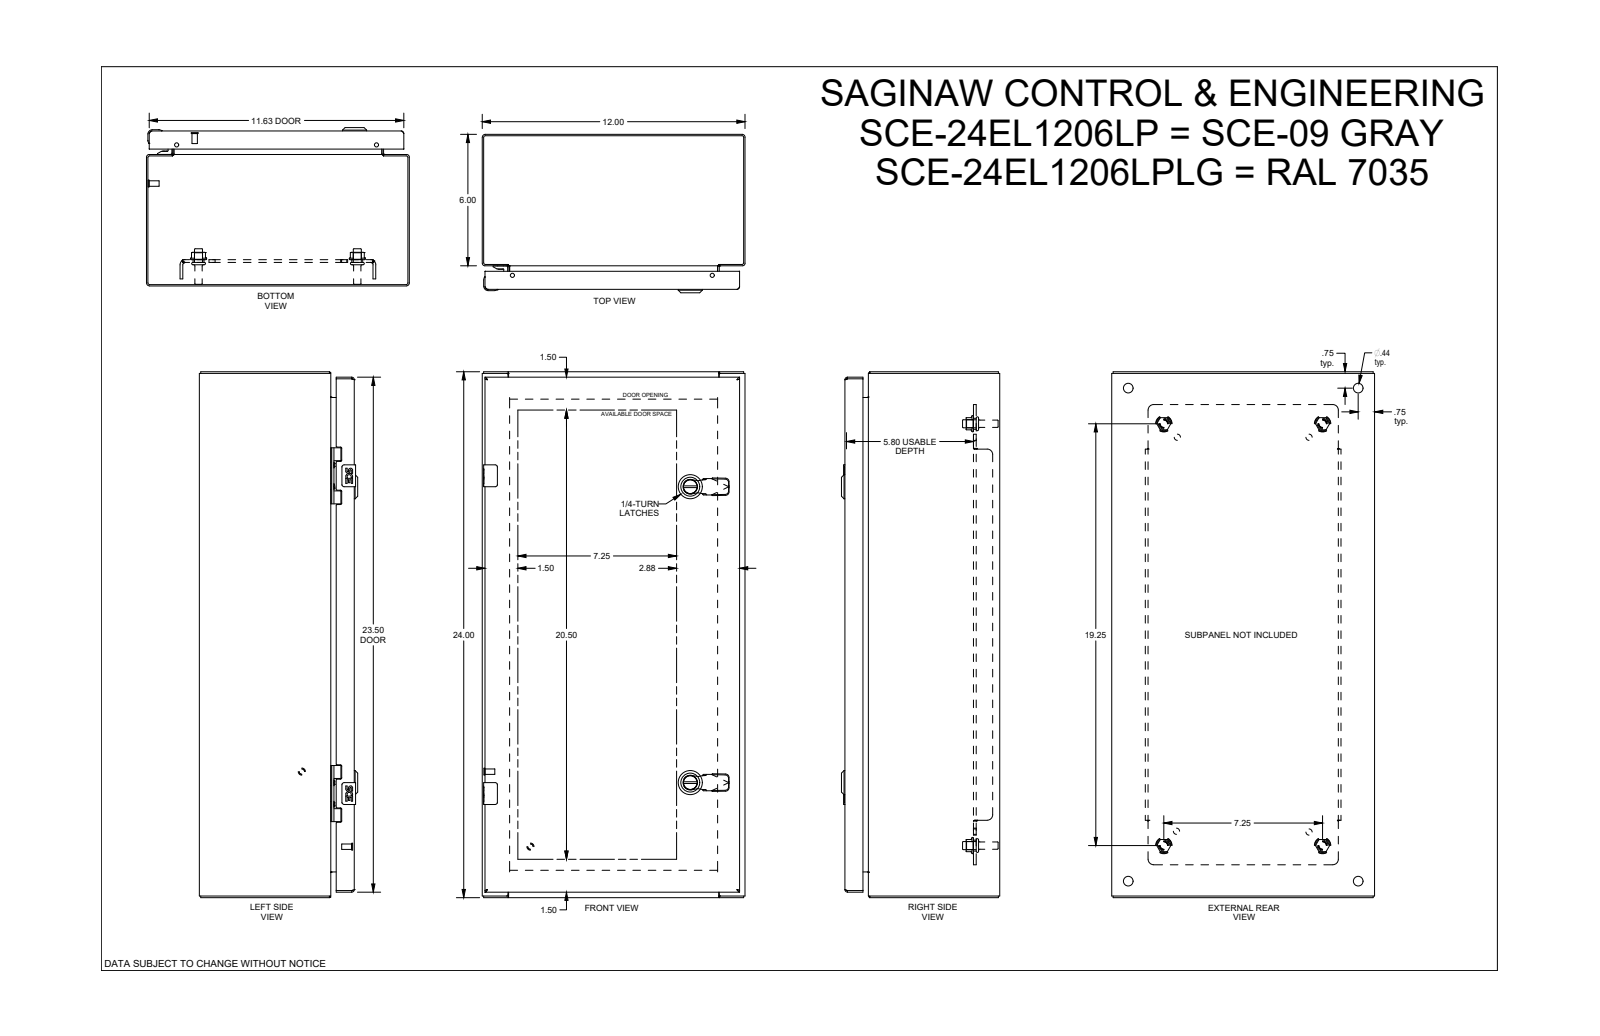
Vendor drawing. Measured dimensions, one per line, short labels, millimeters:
name: SCE-24EL1206LPLG
written by: SolidWorks 2019 (CONFIG_CONTROL_DESIGN)
unit: mm
bodies: 0 solids, 2256 faces (1122 planar, 696 cylindrical, 438 other)
size: 609.6 × 304.8 × 183.6
holes: 4× ⌀4.4, 4× ⌀5.2, 4× ⌀6.2, 4× ⌀6.8, 4× ⌀7.1, 4× ⌀9.3, 4× ⌀9.5, 4× ⌀11.1, 4× ⌀12.7, 2× ⌀1, 2× ⌀4, 2× ⌀4.8
bosses: 6× ⌀4.3, 4× ⌀9.3, 4× ⌀8.4, 4× ⌀6.4, 4× ⌀6.1, 3× ⌀5, 2× ⌀28, 2× ⌀22
rounds: 56× R0.3, 28× R0.3, 28× R0.4, 20× R0.5, 14× R3, 12× R0.6, 12× R1.1, 12× R2.5
face distances: 1.9, 1.9, 175.8, 177.7, 302.9, 179.7, 177.7, 3.2, 25.4, 28.6
hole spacings: 368.3, 25, 0.5, 12.5, 12.5, 22.2, 58.4, 114.1
